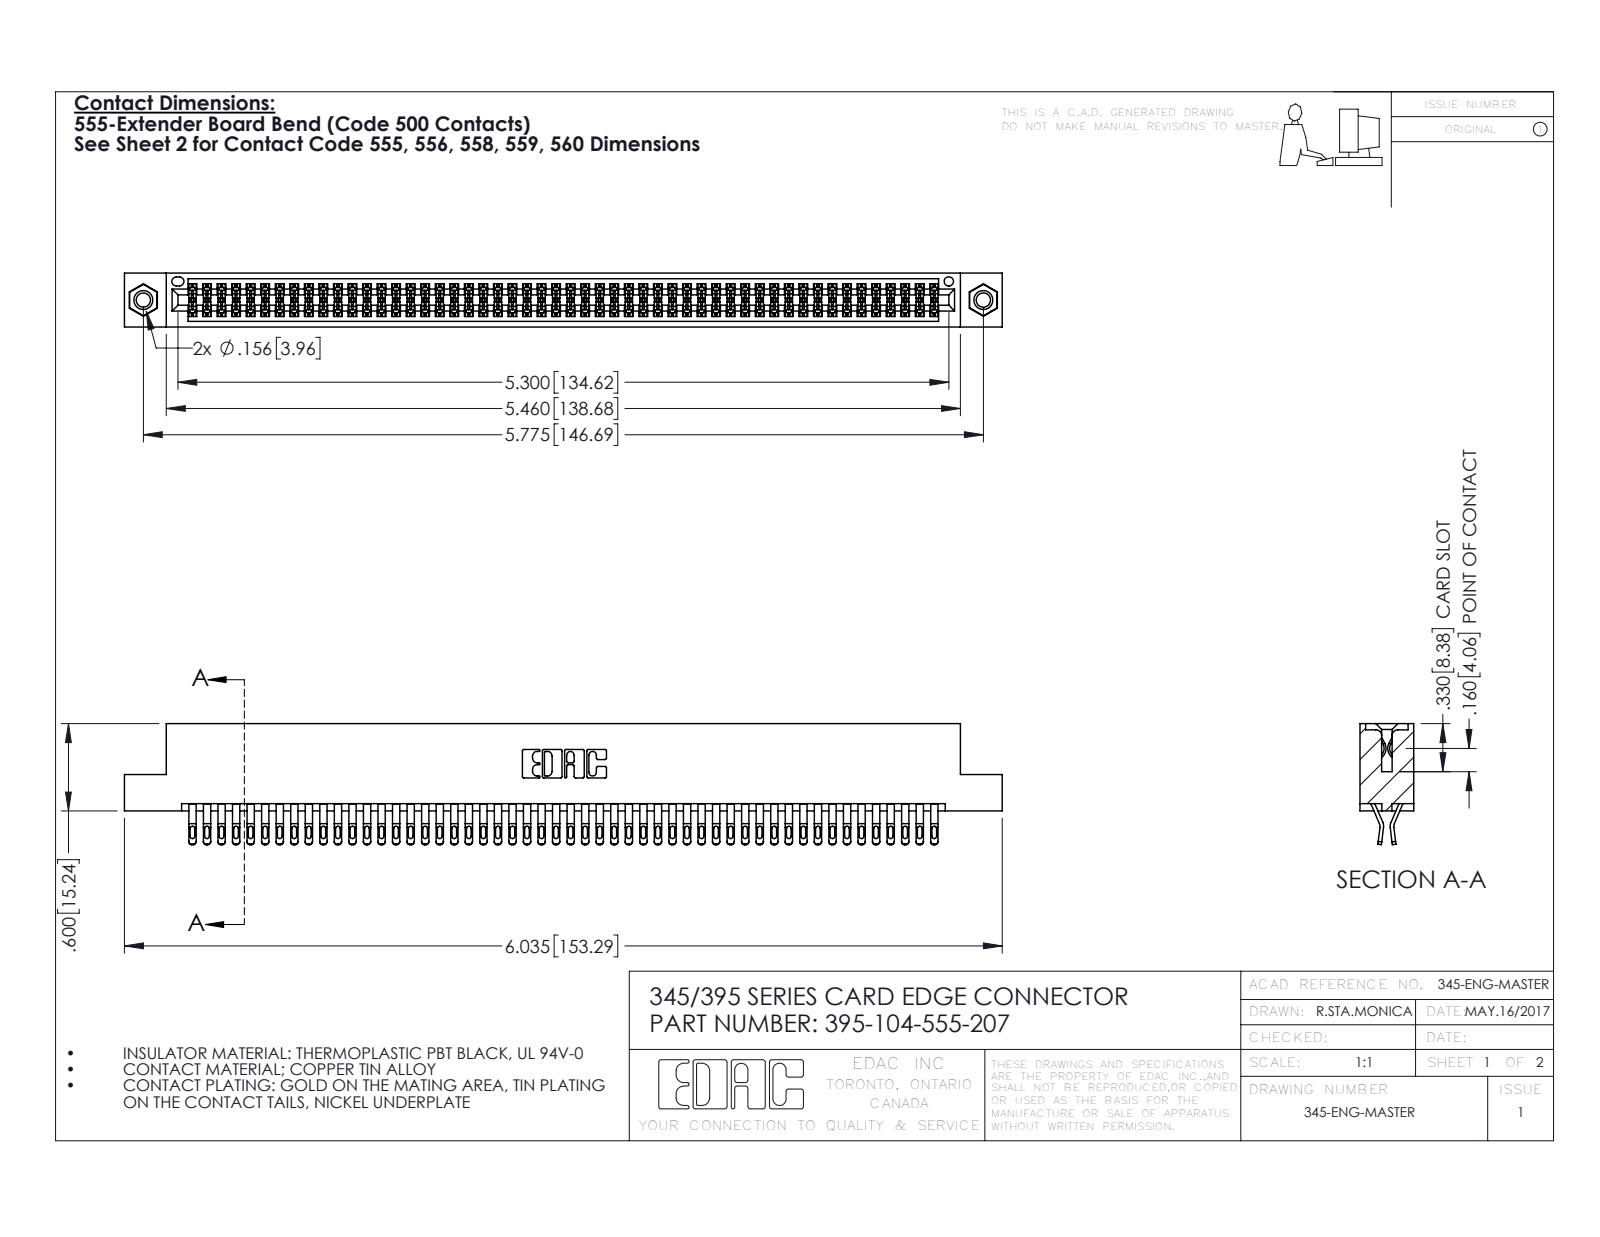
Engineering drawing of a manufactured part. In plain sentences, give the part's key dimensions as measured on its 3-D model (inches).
The part is named "345-292-001_555 Tail; 345-250-001_345-250-005-103; 345 Part_Flush Mounting Lugs - 0.156 Dia-TI; 395-104-555-207". Its 3-D file was written by "SolidWorks 2016 (CONFIG_CONTROL_DESIGN)". It is 107 solids with 6010 faces: 3336 planar, 2658 cylindrical and 16 other. Overall it measures 6.035 by 0.832 by 0.37 inches. Its volume is 0.932 cubic inches and its surface area 36.96 square inches. Round holes: 2 of diameter 0.098, 2 of diameter 0.125, 2 of diameter 0.156, 1 of diameter 0.064. Round bosses or shafts: 2 of diameter 0.155. Partial cylindrical surfaces (rounded edges, fillets, slot ends): 260 of radius 0.016, 208 of radius 0.02, 156 of radius 0.006, 22 of radius 0.01, 6 of radius 0.007, 6 of radius 0.031, 3 of radius 0.026, 2 of radius 0.01. The main face-to-face distances are 0.072, 0.298, 0.025, 0.37, 0.2, 0.098, 0.272, 0.225, 0.175, 0.149. The hole center spacings are 0.27, 5.539, 5.775.
